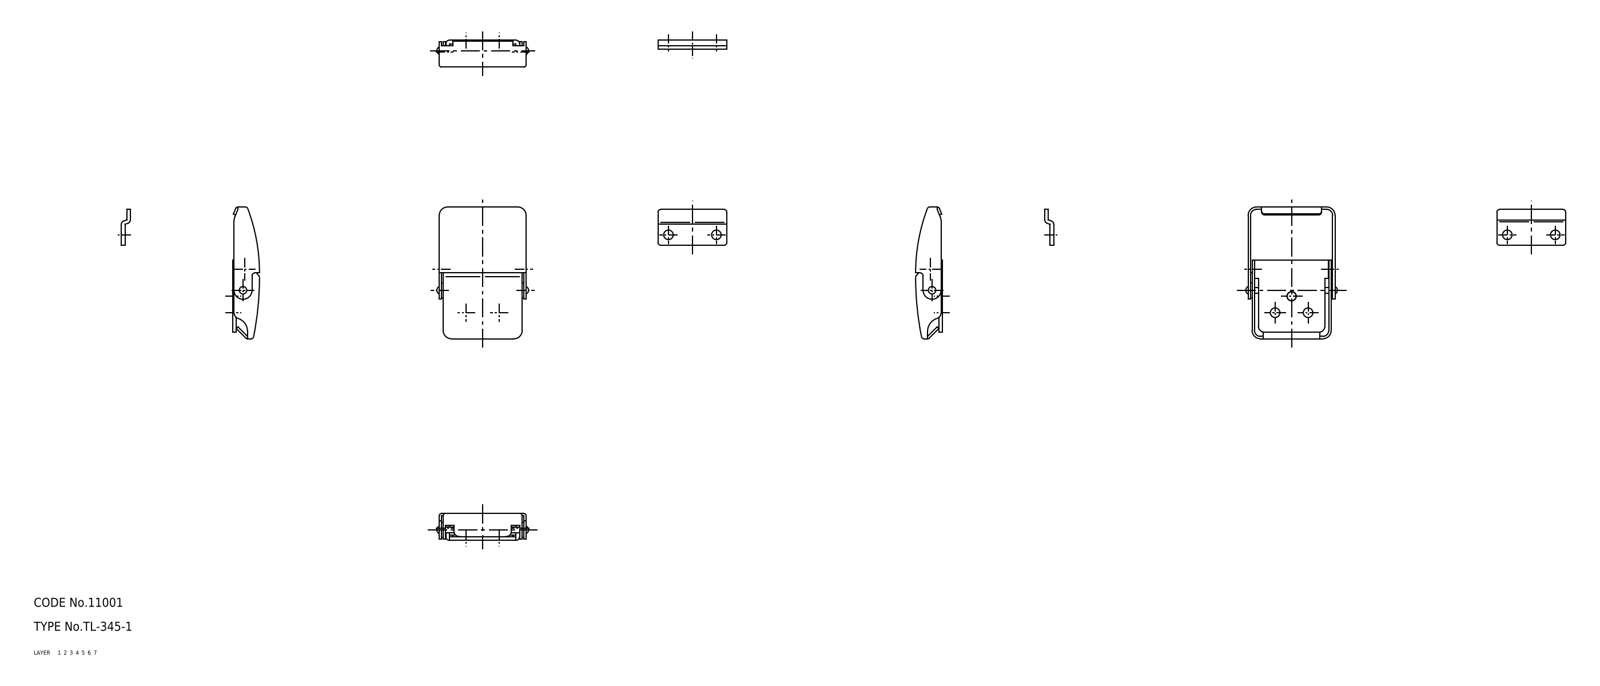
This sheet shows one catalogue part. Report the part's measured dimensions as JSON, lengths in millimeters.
{"part_name": "washer; shaft_B; shaft_A; rivet (+6 more)", "step_written_by": "CADfix (AUTOMOTIVE_DESIGN)", "units": "millimeters", "bodies": {"solids": 10, "faces": 220, "planar": 0, "cylindrical": 0, "other": 220}, "overall_size": [44, 30.6, 9], "volume_mm3": 3154, "surface_area_mm2": 7793}
